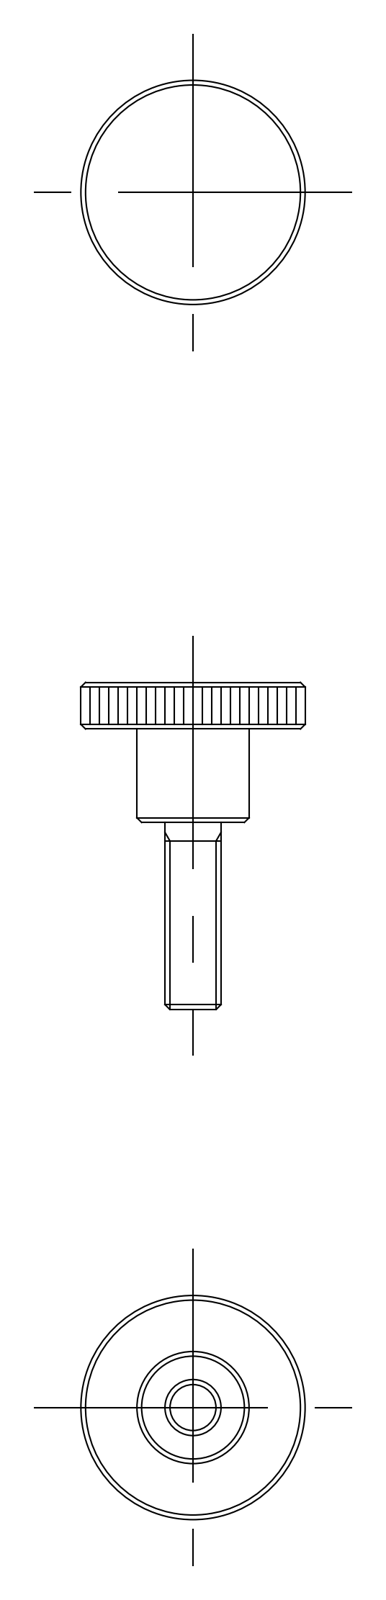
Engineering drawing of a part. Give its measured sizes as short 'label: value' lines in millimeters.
name: knob
written by: CADfix (AUTOMOTIVE_DESIGN)
unit: mm
bodies: 1 solid, 18 faces (0 planar, 0 cylindrical, 18 other)
size: 35 × 24 × 24
volume: 3 940 mm³; area: 1 974 mm²
